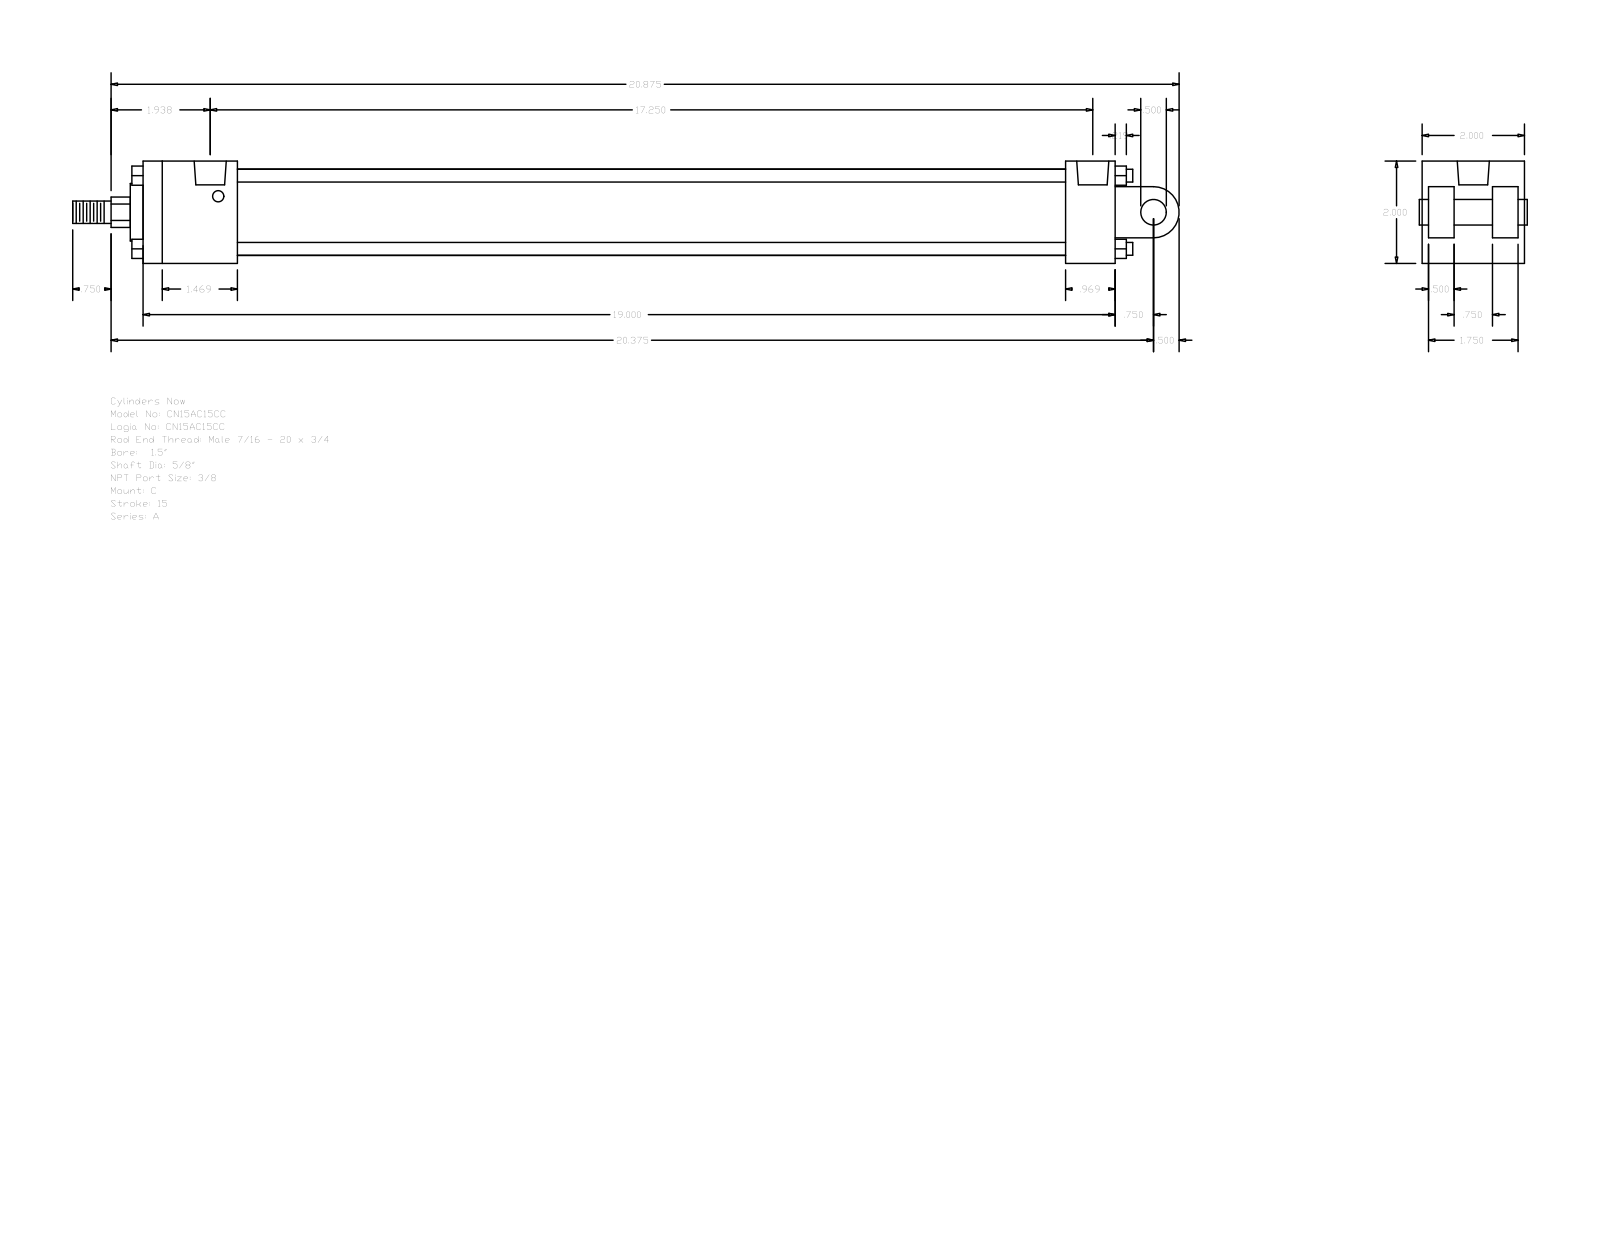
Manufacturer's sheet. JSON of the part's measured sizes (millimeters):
{"part_name": "A_C__0150_0.625", "step_written_by": "GSSL Pune (CONFIG_CONTROL_DESIGN)", "units": "millimeters", "bodies": {"solids": 0, "faces": 135, "planar": 102, "cylindrical": 33, "other": 0}, "overall_size": [549.27, 50.8, 50.8], "round_holes": [[5.56, 4], [15.93, 2]], "round_bosses_or_shafts": [[6.35, 4], [42.93, 1], [28.57, 1], [15.88, 1], [12.7, 1], [11.11, 1]], "partial_cylinders_radius": [[7.54, 1], [12.7, 1]], "face_to_face_distances": [50.8, 12.7, 482.6, 34.93, 3.17, 15.87, 47.63, 31.76, 457.99, 24.61], "hole_center_spacings": [3.97, 430.21, 434.18, 438.15]}
